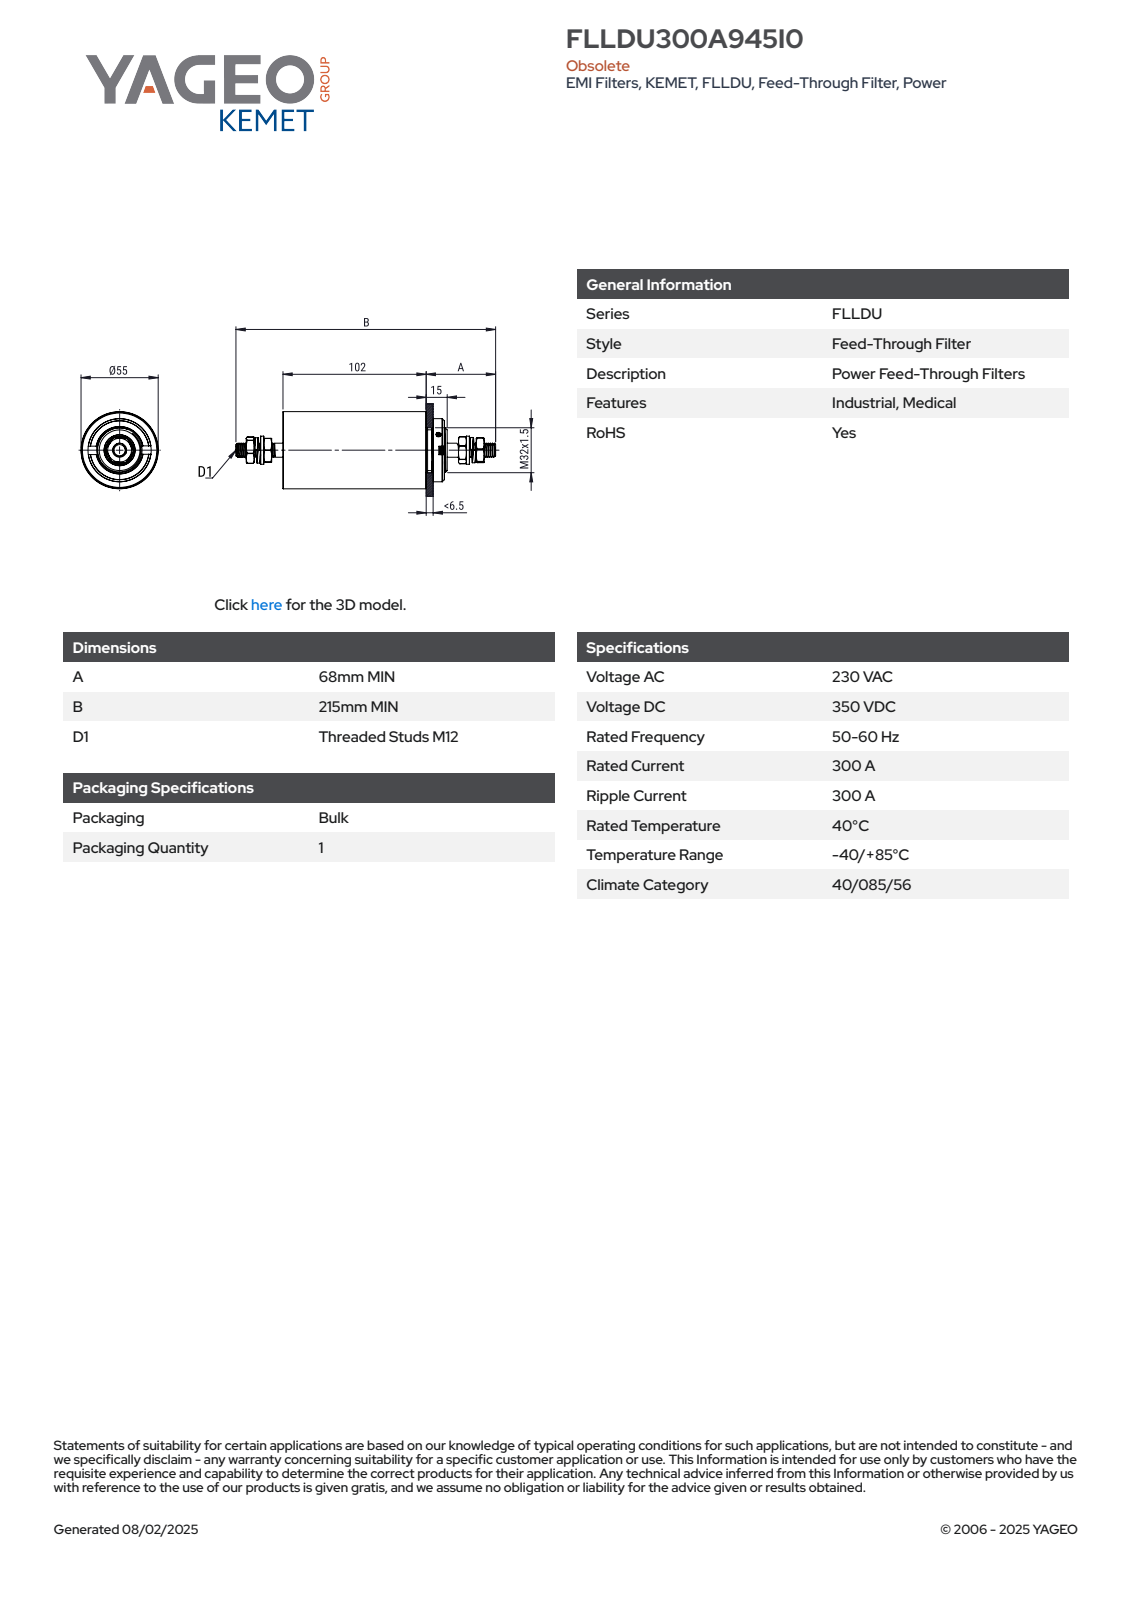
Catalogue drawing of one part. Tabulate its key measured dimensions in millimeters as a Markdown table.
| quantity | value |
| --- | --- |
| part name | GEH0062; GEH0028; LOCK WASHER M12_91169A214; HEX NUT M12x1.75 THIN_90370A103 (+5 more) |
| STEP written by | SolidWorks 2021 (AUTOMOTIVE_DESIGN) |
| units | millimeters |
| bodies | 14 solids, 444 faces (63 planar, 208 cylindrical, 173 other) |
| overall size | 215 × 55 × 55 |
| volume | 72 858 mm³ |
| surface area | 69 907 mm² |
| round holes (diameter × count) | 13 × 1, 22 × 1, 30.7 × 1, 53 × 1 |
| round bosses / shafts (diameter × count) | 55 × 1, 54 × 1, 45 × 1, 32 × 1, 29 × 1, 24 × 1, 22.1 × 1, 12 × 1 |
| partial cylindrical surfaces (radius × count) | 0.5 × 24 |
| main face-to-face distances | 4, 102, 98, 111, 13, 103, 115, 8, 5, 107 |
